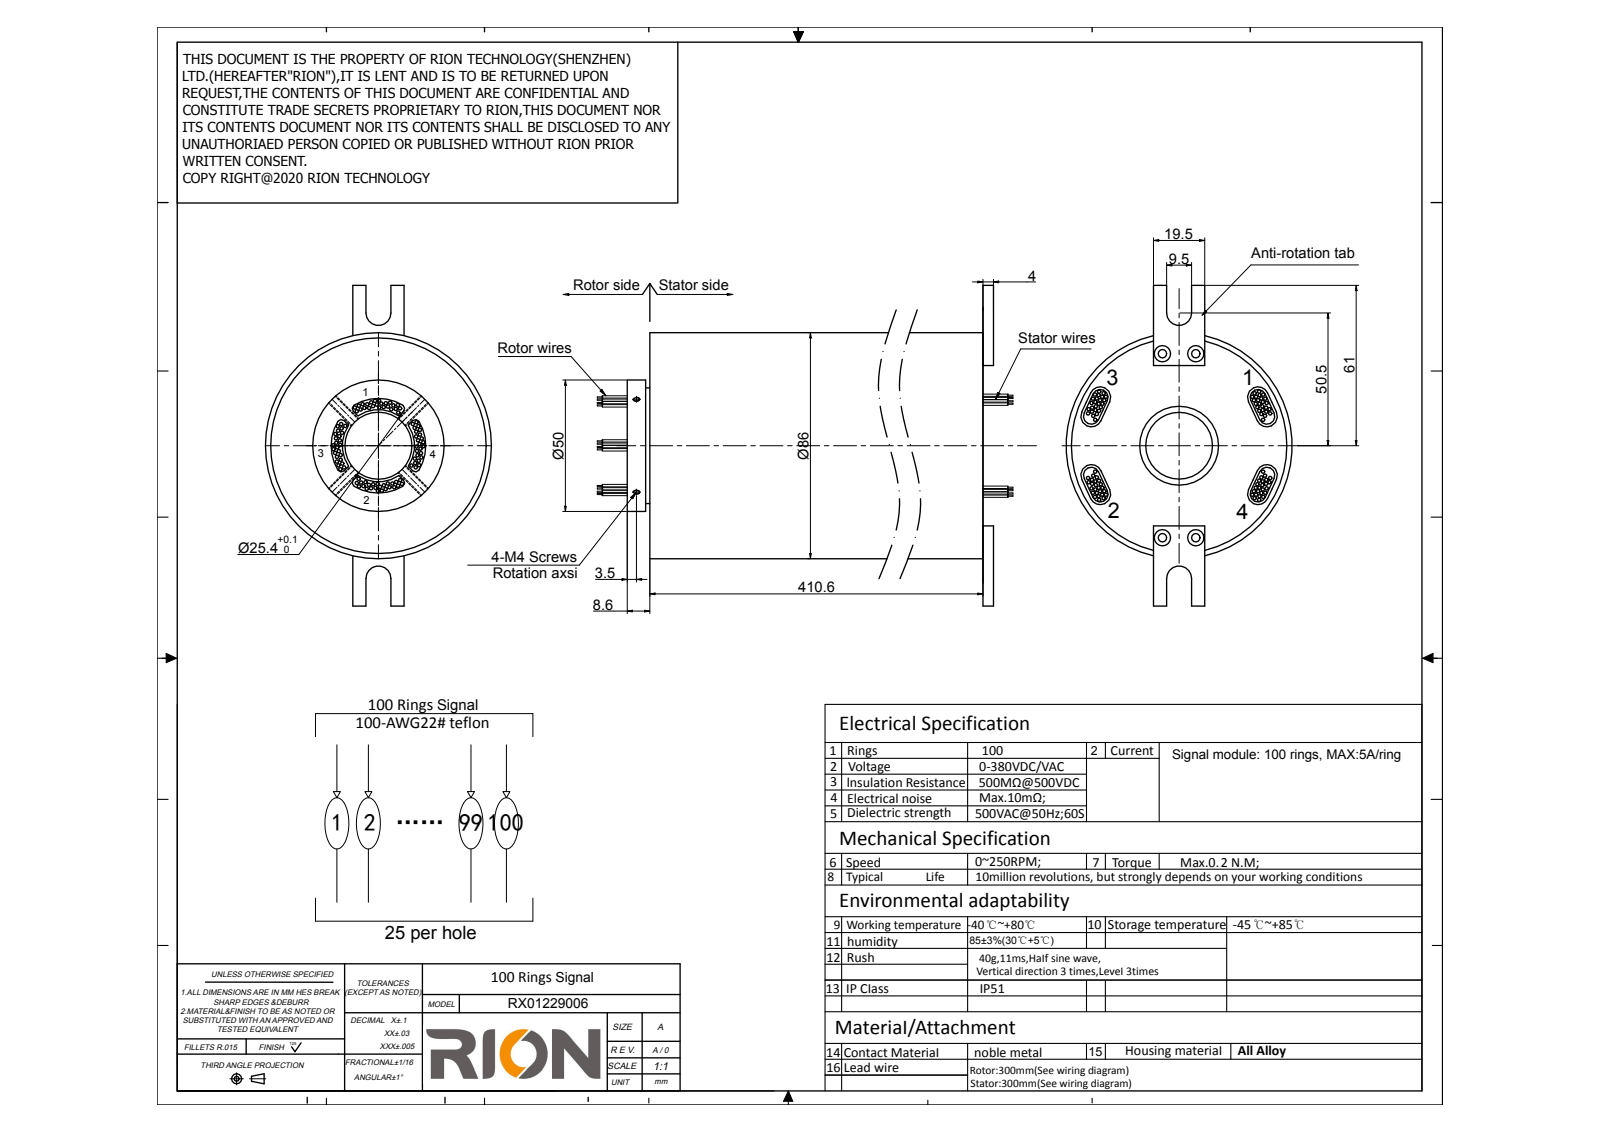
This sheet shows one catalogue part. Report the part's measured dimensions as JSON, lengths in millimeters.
{"step_written_by": "SolidWorks 2014 (CONFIG_CONTROL_DESIGN)", "units": "millimeters", "bodies": {"solids": 1, "faces": 750, "planar": 251, "cylindrical": 483, "other": 16}, "overall_size": [438.2, 122, 86], "volume_mm3": 2194000, "surface_area_mm2": 174127, "round_holes": [[2.5, 4], [3.2, 4], [3.3, 4], [25.4, 1], [30, 1], [82, 1]], "round_bosses_or_shafts": [[1.3, 200], [86, 1], [81.9, 1], [81.8, 1], [50, 1], [44, 1], [29.9, 1]], "partial_cylinders_radius": [[2.75, 8], [3, 8], [4.75, 2], [14, 1], [19.5, 1]], "face_to_face_distances": [410.6, 8.6, 419.2, 4, 423.2, 414.6, 7, 1.6, 412.2, 416.2], "hole_center_spacings": [35.57, 12.7, 70, 71.14]}
